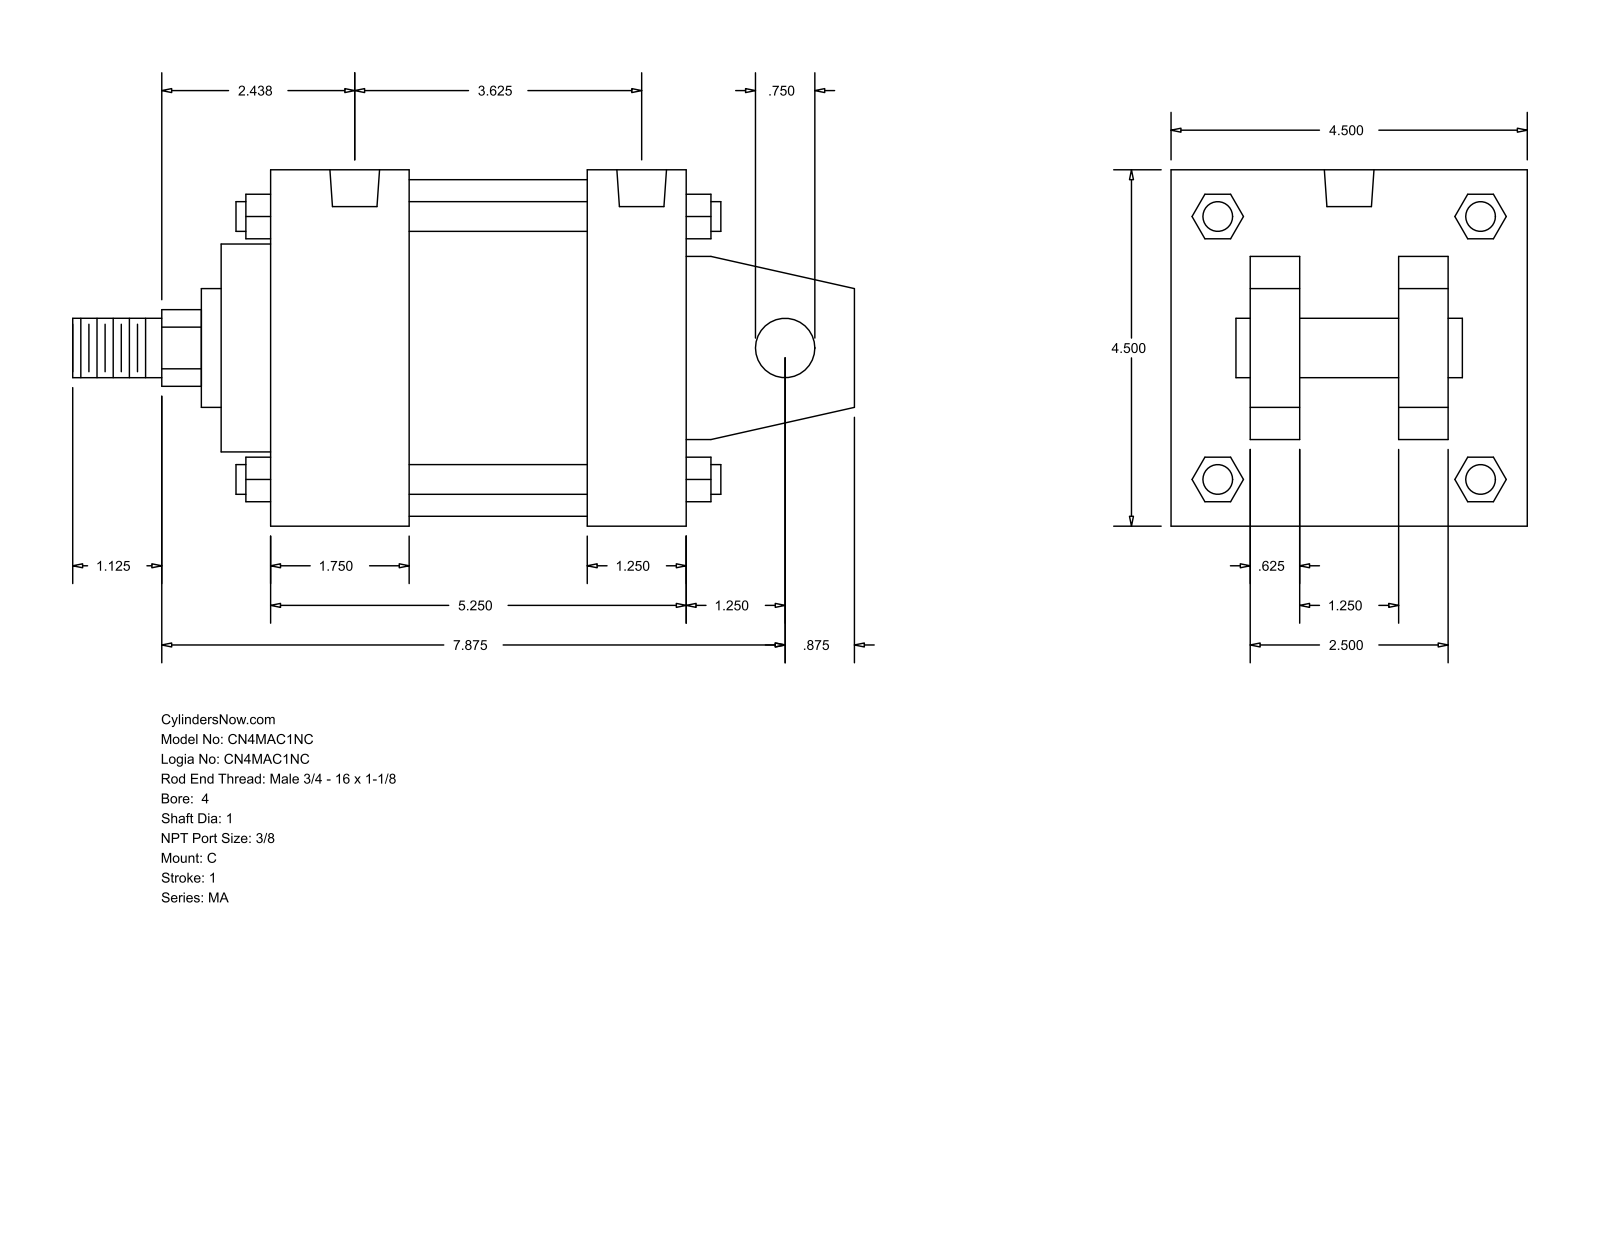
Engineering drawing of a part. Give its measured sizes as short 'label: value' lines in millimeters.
name: MA_C__0400_1
written by: GSSL Pune (CONFIG_CONTROL_DESIGN)
unit: mm
bodies: 0 solids, 141 faces (109 planar, 32 cylindrical, 0 other)
size: 250.82 × 114.3 × 114.3
holes: 4× ⌀11.11, 2× ⌀15.93
bosses: 4× ⌀9.53, 2× ⌀19.05, 1× ⌀107.95, 1× ⌀66.67, 1× ⌀38.1, 1× ⌀25.4
rounds: 1× R12.29
face distances: 114.3, 133.36, 88.9, 15.87, 73.03, 41.27, 25.4, 47.63, 101.61, 31.75
hole spacings: 82.55, 4.76, 4.77, 87.31, 87.32, 92.08
